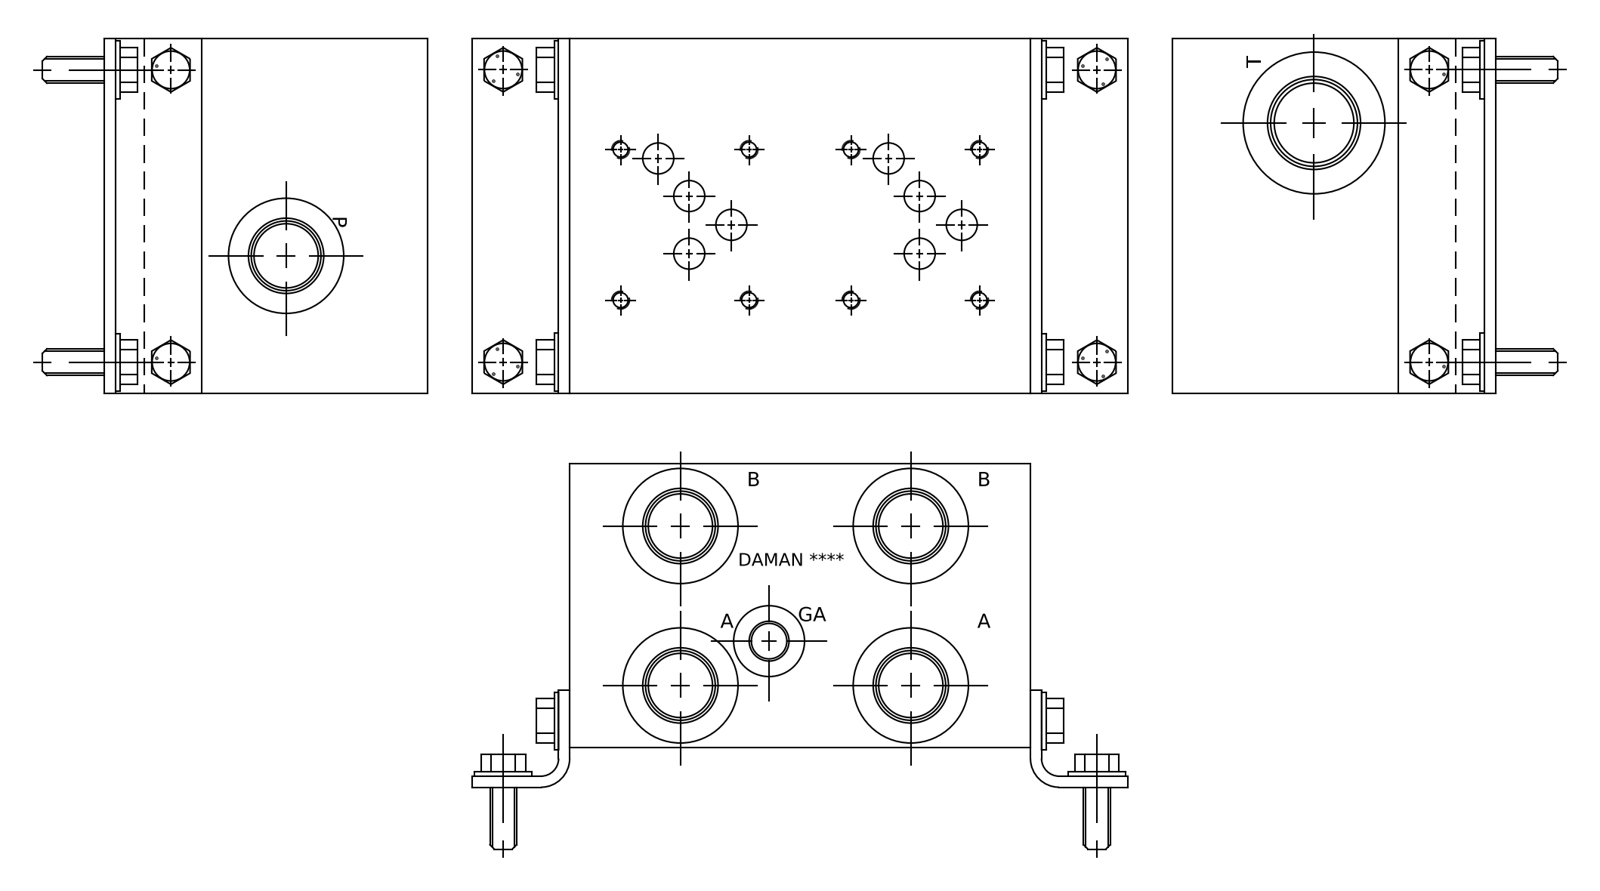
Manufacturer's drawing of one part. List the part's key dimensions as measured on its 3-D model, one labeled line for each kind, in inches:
Part name (STEP PRODUCT): Part__3D
STEP written by: Autodesk Inventor 2020 (AUTOMOTIVE_DESIGN)
Units: inches
Bodies: 1 solid, 621 faces (337 planar, 69 cylindrical, 215 other)
Overall size (bounding box): 6.5 × 5 × 4
Volume: 121.6 in³ · Surface area: 194.5 in²
Round holes (diameter × count): ⌀0.197 ×8, ⌀0.236 ×8, ⌀0.438 ×8, ⌀0.906 ×5, ⌀0.981 ×5, ⌀1.08 ×5, ⌀1.655 ×5, ⌀1.063 ×4, ⌀0.312 ×2, ⌀0.375 ×2, ⌀0.688 ×2, ⌀0.484 ×1
Main face-to-face distances: 4, 6.5, 5, 0.031, 4.969, 6.469, 6.438, 0.75, 0.781, 4.219
Hole centre spacings: 3.25, 1.813, 2.125, 0.547, 0.72, 0.72, 1.069, 1.171
